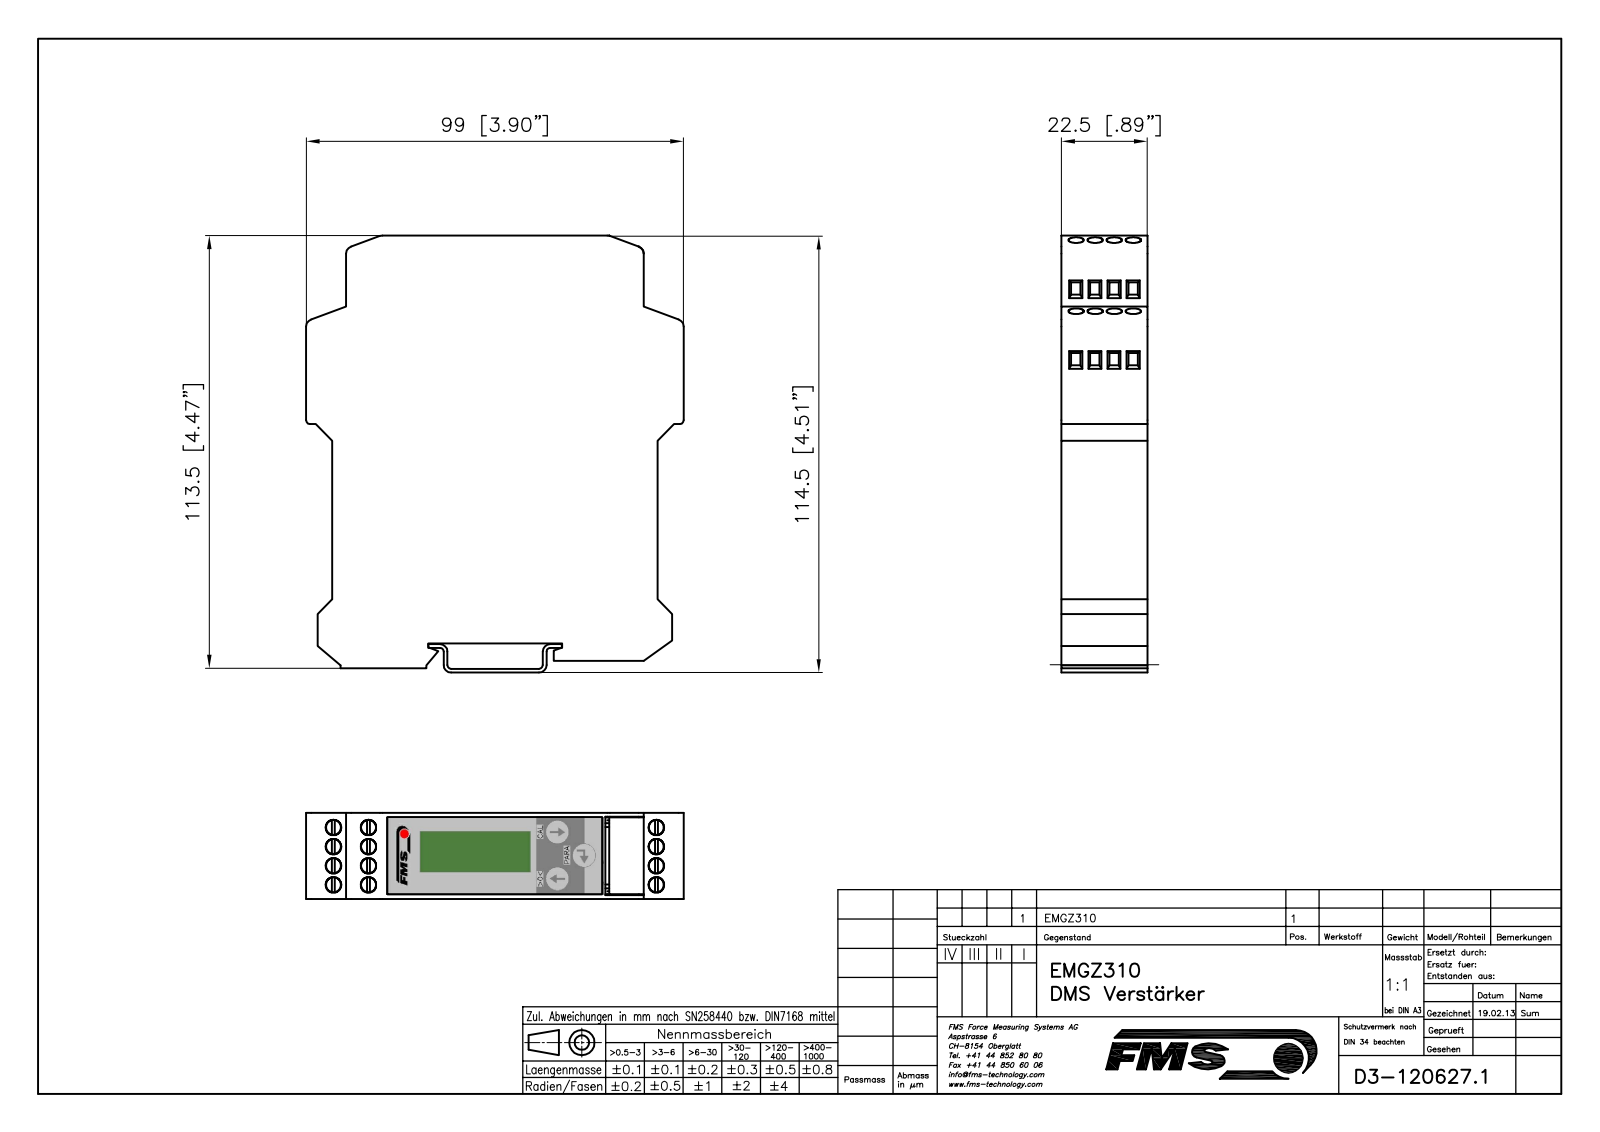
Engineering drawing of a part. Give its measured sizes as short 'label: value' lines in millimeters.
name: 120627.1; E1206275; E1206272; GLAS_EMGZ310_OBERSEITE (+8 more)
written by: Mechanical Desktop 2009 (CONFIG_CONTROL_DESIGN)
unit: mm
bodies: 24 solids, 771 faces (595 planar, 128 cylindrical, 48 other)
size: 114.62 × 99 × 22.5
volume: 90 564 mm³; area: 72 913 mm²
holes: 12× ⌀1.7, 12× ⌀4.05
bosses: 12× ⌀3.95, 12× ⌀2.5
rounds: 16× R2, 6× R1, 4× R2.02, 1× R0.5, 1× R1.1, 1× R1.9
face distances: 1.5, 21, 22.5, 3.35, 19.15, 4.95, 1.6, 17.55, 1.85, 17.65
hole spacings: 5, 10, 10.46, 15, 50.05, 75.68, 84.85, 9.19
